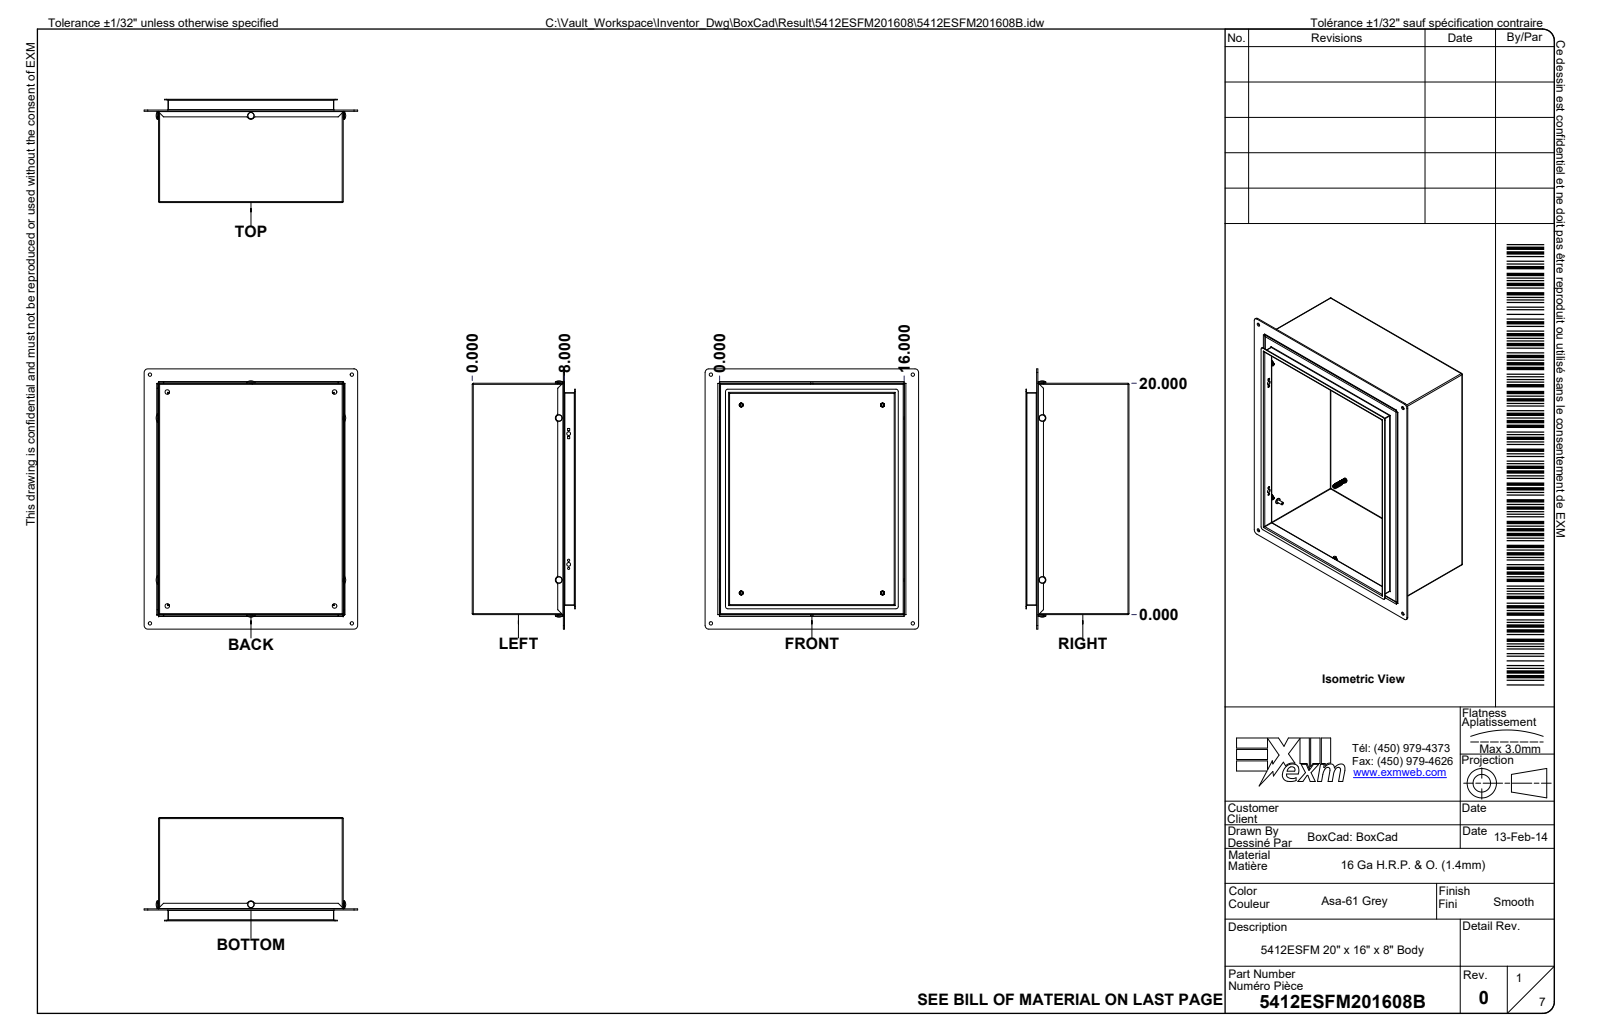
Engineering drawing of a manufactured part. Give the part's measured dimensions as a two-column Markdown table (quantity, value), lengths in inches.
| quantity | value |
| --- | --- |
| part name | 5412ESFM201608; 5412ESFM201608B; 5412ESFM201608B-P; STK-Q-16005 (+8 more) |
| STEP written by | Autodesk Inventor 2024 (AUTOMOTIVE_DESIGN) |
| units | inches |
| bodies | 95 solids, 10811 faces (3221 planar, 2870 cylindrical, 4720 other) |
| overall size | 22.5 × 18.5 × 9.31 |
| volume | 123.4 in³ |
| surface area | 3 835 in² |
| round holes (diameter × count) | 0.165 × 32, 0.201 × 11, 0.29 × 11, 0.315 × 11, 0.03 × 9, 0.043 × 8, 0.197 × 7, 0.268 × 7, 0.311 × 6, 0.178 × 4, 0.27 × 4, 0.39 × 4 |
| round bosses / shafts (diameter × count) | 0.237 × 32, 0.232 × 12, 0.03 × 9, 0.039 × 8, 0.374 × 7, 0.717 × 4, 0.311 × 4, 0.262 × 4 |
| partial cylindrical surfaces (radius × count) | 0.02 × 349, 0.01 × 139, 0.008 × 114, 0.039 × 101, 0.012 × 50, 0.016 × 30, 0.031 × 28, 0.084 × 24 |
| main face-to-face distances | 0.053, 9.081, 9.028, 15.947, 9.135, 0.927, 0.874, 8.154, 8.207, 1.032 |
| hole center spacings | 1.969, 0.984, 11.303, 2.953, 3.937, 0.35, 0.735, 1.052 |
